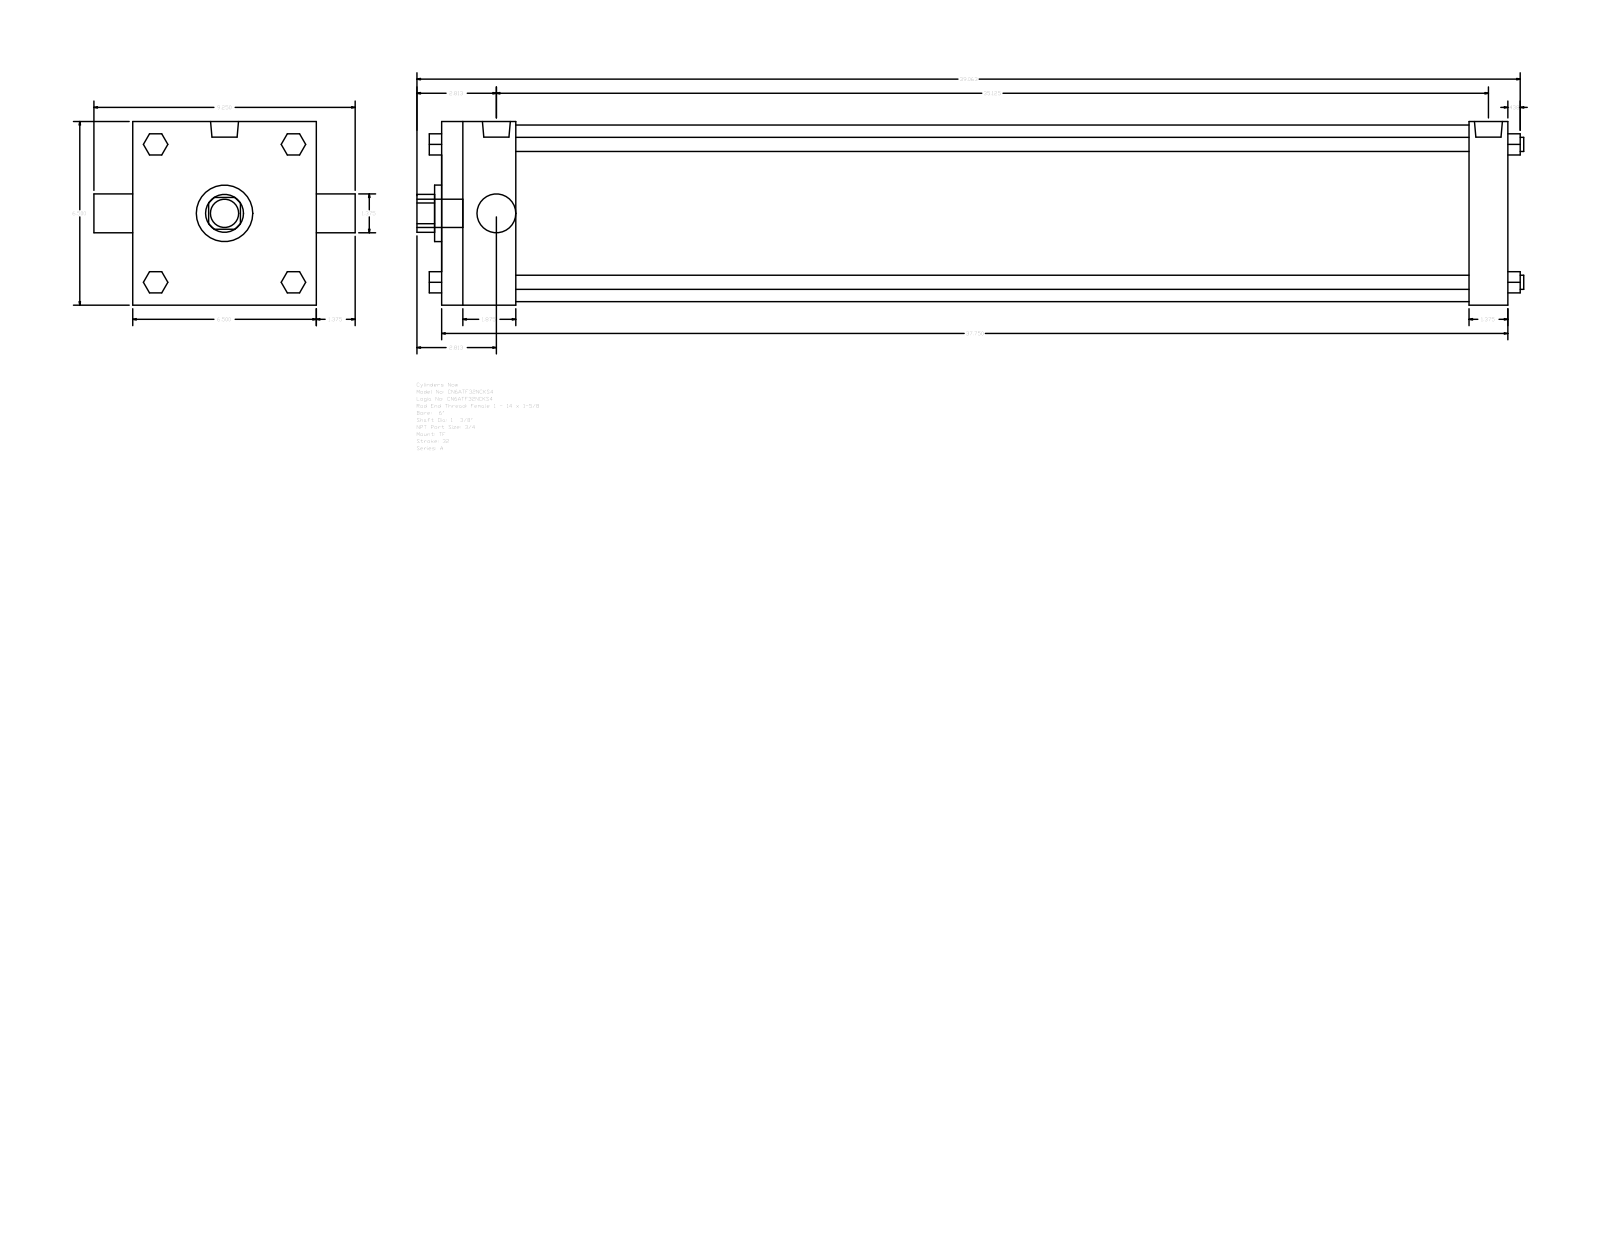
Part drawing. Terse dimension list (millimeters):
name: A_TF__0600_1.375
written by: GSSL Pune (CONFIG_CONTROL_DESIGN)
unit: mm
bodies: 0 solids, 120 faces (92 planar, 28 cylindrical, 0 other)
size: 995.36 × 234.95 × 165.1
holes: 2× ⌀34.92, 1× ⌀50.8, 1× ⌀158.75
bosses: 4× ⌀12.7, 3× ⌀15.08, 2× ⌀25.12, 1× ⌀25.4
rounds: 1× R17.06
face distances: 165.1, 958.85, 66.67, 892.18, 923.92, 857.25, 34.93, 19.05, 61.97, 107.34
